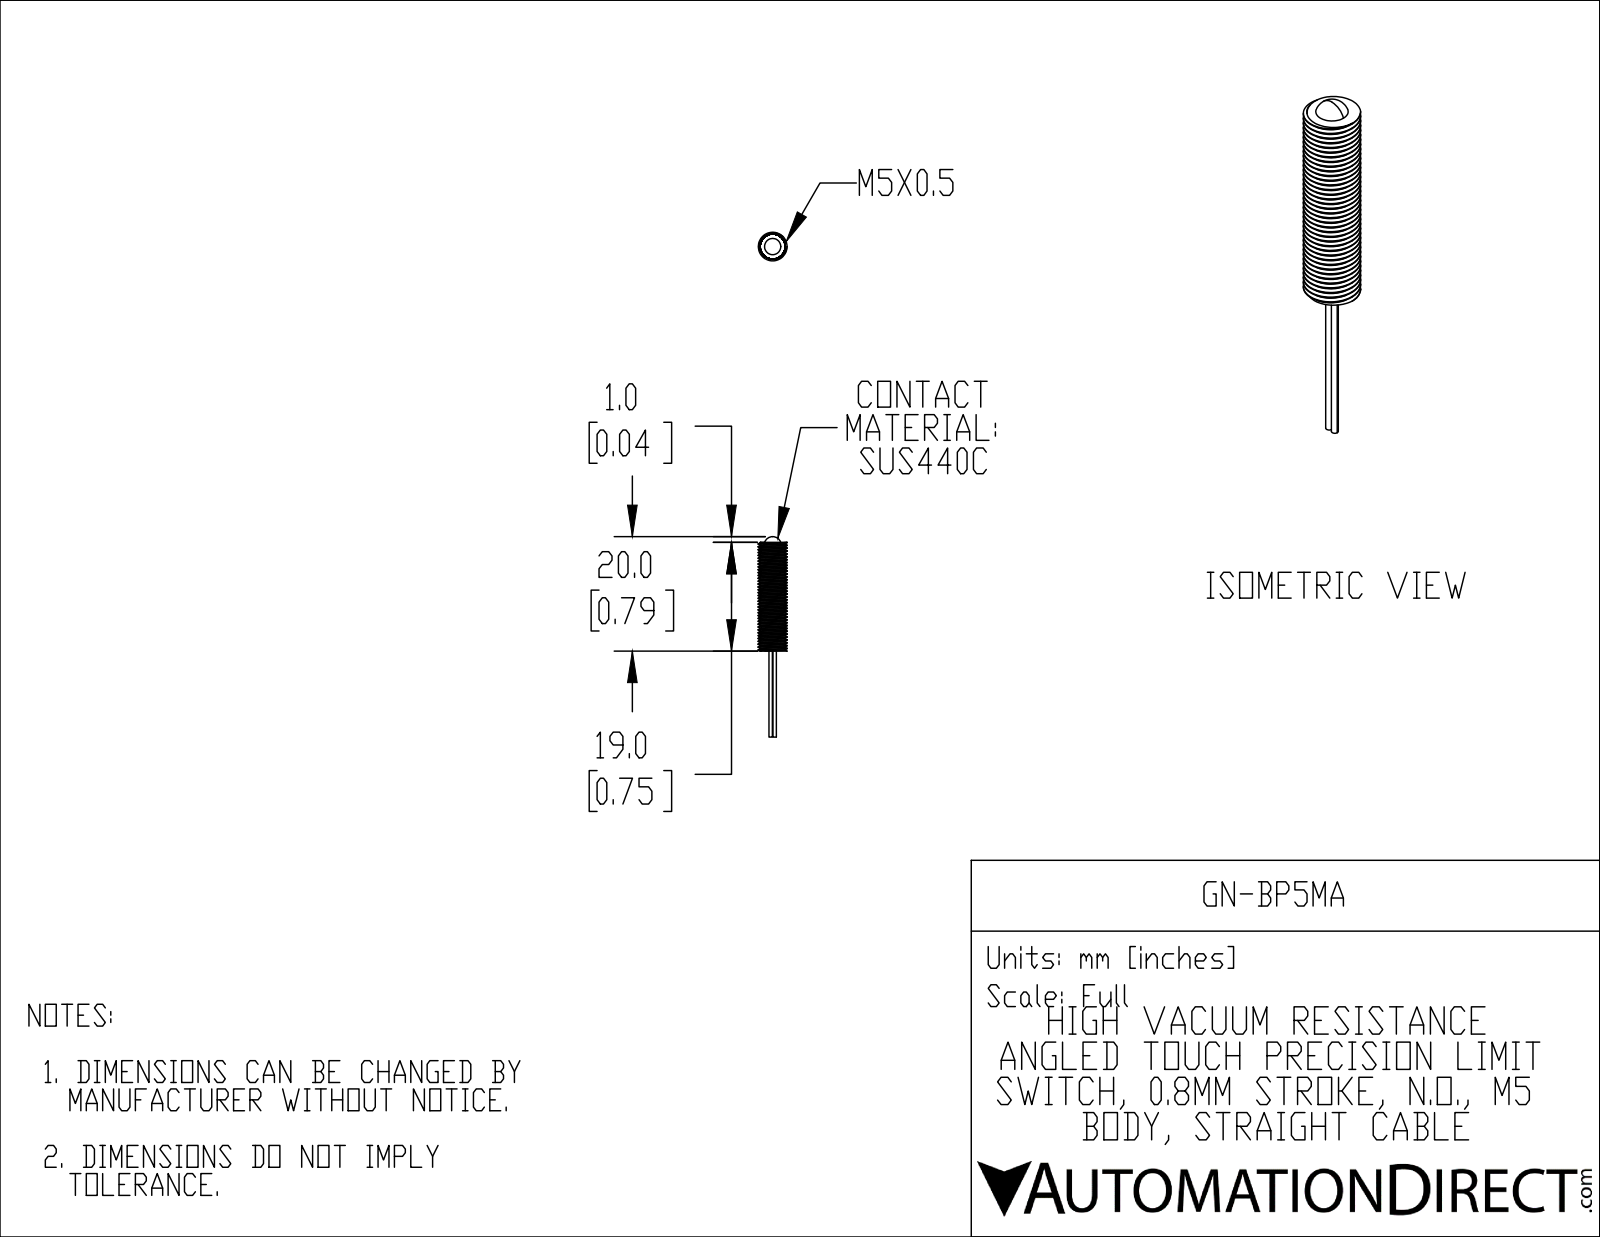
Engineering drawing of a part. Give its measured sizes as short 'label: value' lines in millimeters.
name: GN-BP5MA
written by: SolidWorks 2020 (CONFIG_CONTROL_DESIGN)
unit: mm
bodies: 1 solid, 90 faces (4 planar, 81 cylindrical, 5 other)
size: 35 × 5 × 5
volume: 339 mm³; area: 595 mm²
bosses: 2× ⌀0.6, 1× ⌀5
face distances: 19, 34, 15
